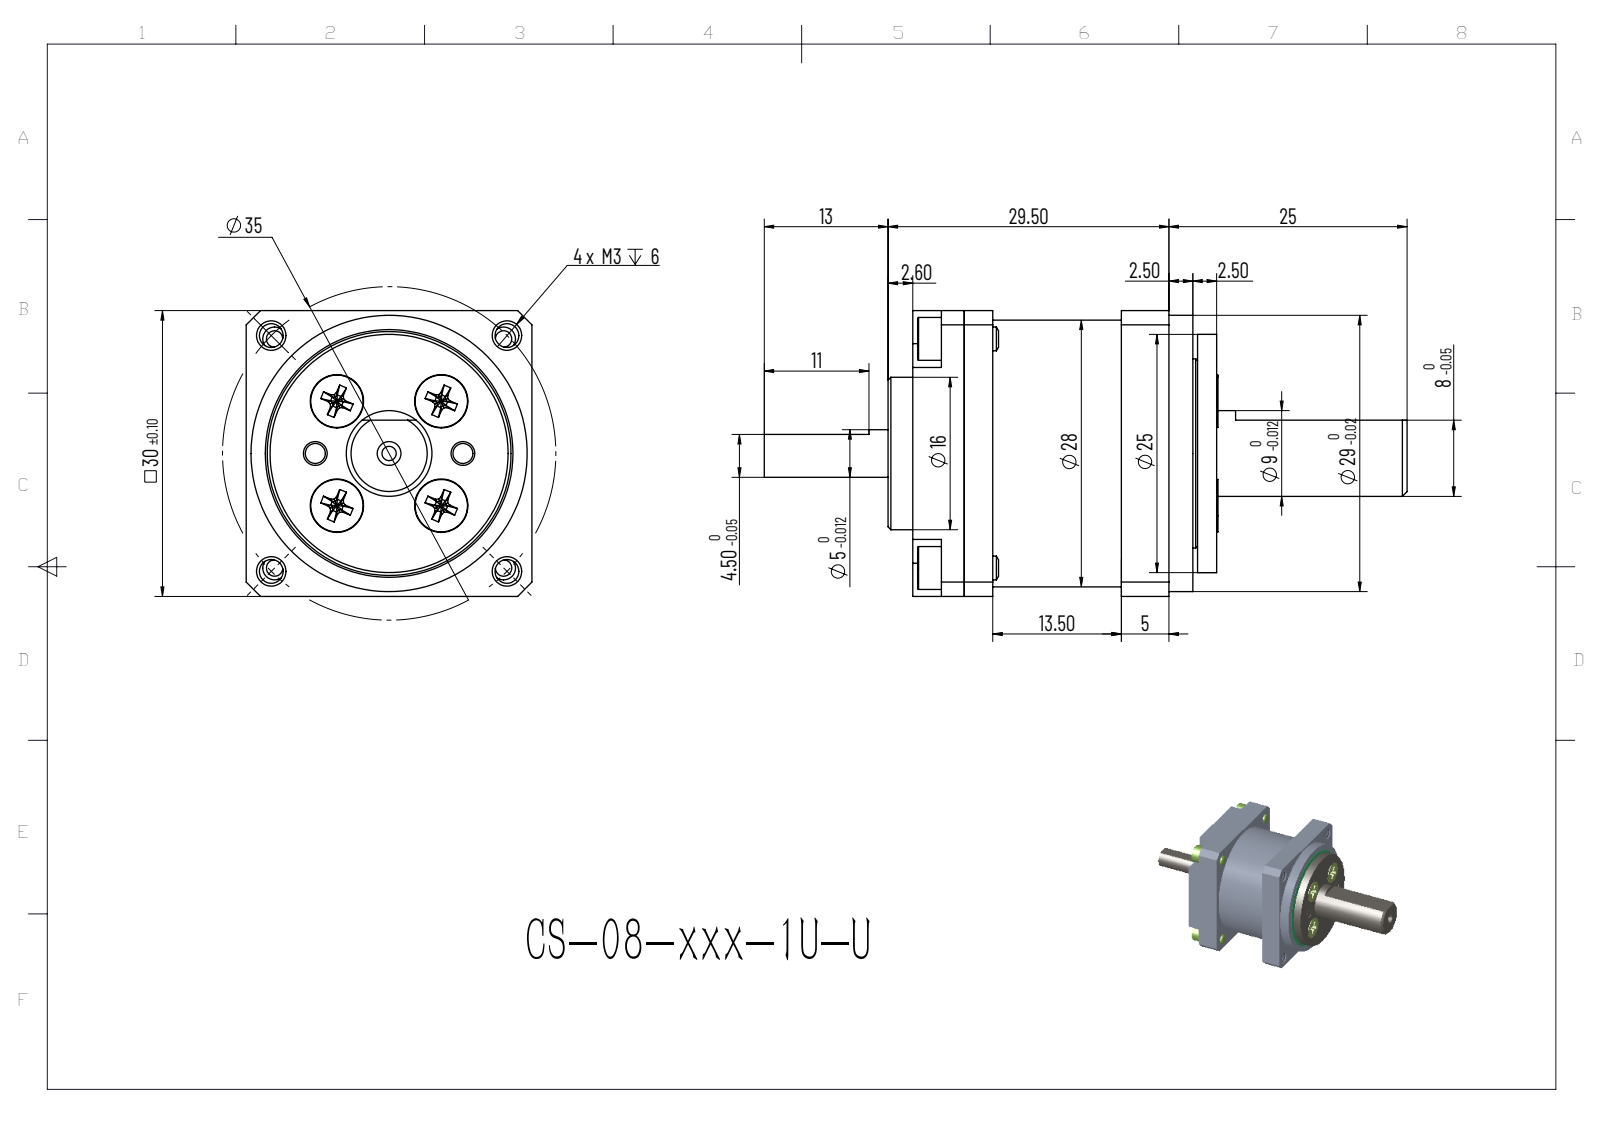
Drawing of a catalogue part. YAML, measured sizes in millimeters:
part_name: "CS-08-1U-U; CSF-08-1U-07_??; ?? 2.5x5_??; CSF-08-1U-04_?? (+8 more)"
step_written_by: "ONSHAPE BY PTC INC, 1.203 (AP242_MANAGED_MODEL_BASED_3D_ENGINEERING_MIM_LF)"
units: millimeters
bodies: {solids: 51, faces: 750, planar: 356, cylindrical: 223, other: 171}
overall_size: [67.5, 30, 30]
volume: 22889
surface_area: 23648
round_holes:
  - {diameter: 2.5, count: 10}
  - {diameter: 1.25, count: 4}
  - {diameter: 2.05, count: 4}
  - {diameter: 2.7, count: 4}
  - {diameter: 3, count: 4}
  - {diameter: 1, count: 1}
  - {diameter: 1.5, count: 1}
  - {diameter: 2, count: 1}
  - {diameter: 3.3, count: 1}
  - {diameter: 5, count: 1}
  - {diameter: 6, count: 1}
  - {diameter: 7.7, count: 1}
round_bosses_or_shafts:
  - {diameter: 5.5, count: 4}
  - {diameter: 4.5, count: 4}
  - {diameter: 2.6, count: 4}
  - {diameter: 2.5, count: 4}
  - {diameter: 29, count: 1}
  - {diameter: 28, count: 1}
  - {diameter: 26, count: 1}
  - {diameter: 25, count: 1}
partial_cylinders:
  - {radius: 2.5, count: 4}
  - {radius: 5.6, count: 1}
face_to_face_distances: [2.5, 5.5, 3, 14.5, 10, 5, 2, 21, 24.5, 8]
hole_center_spacings: [6.8, 12.28, 12.7, 15.95, 18.68, 19.13, 24.39, 24.65]
